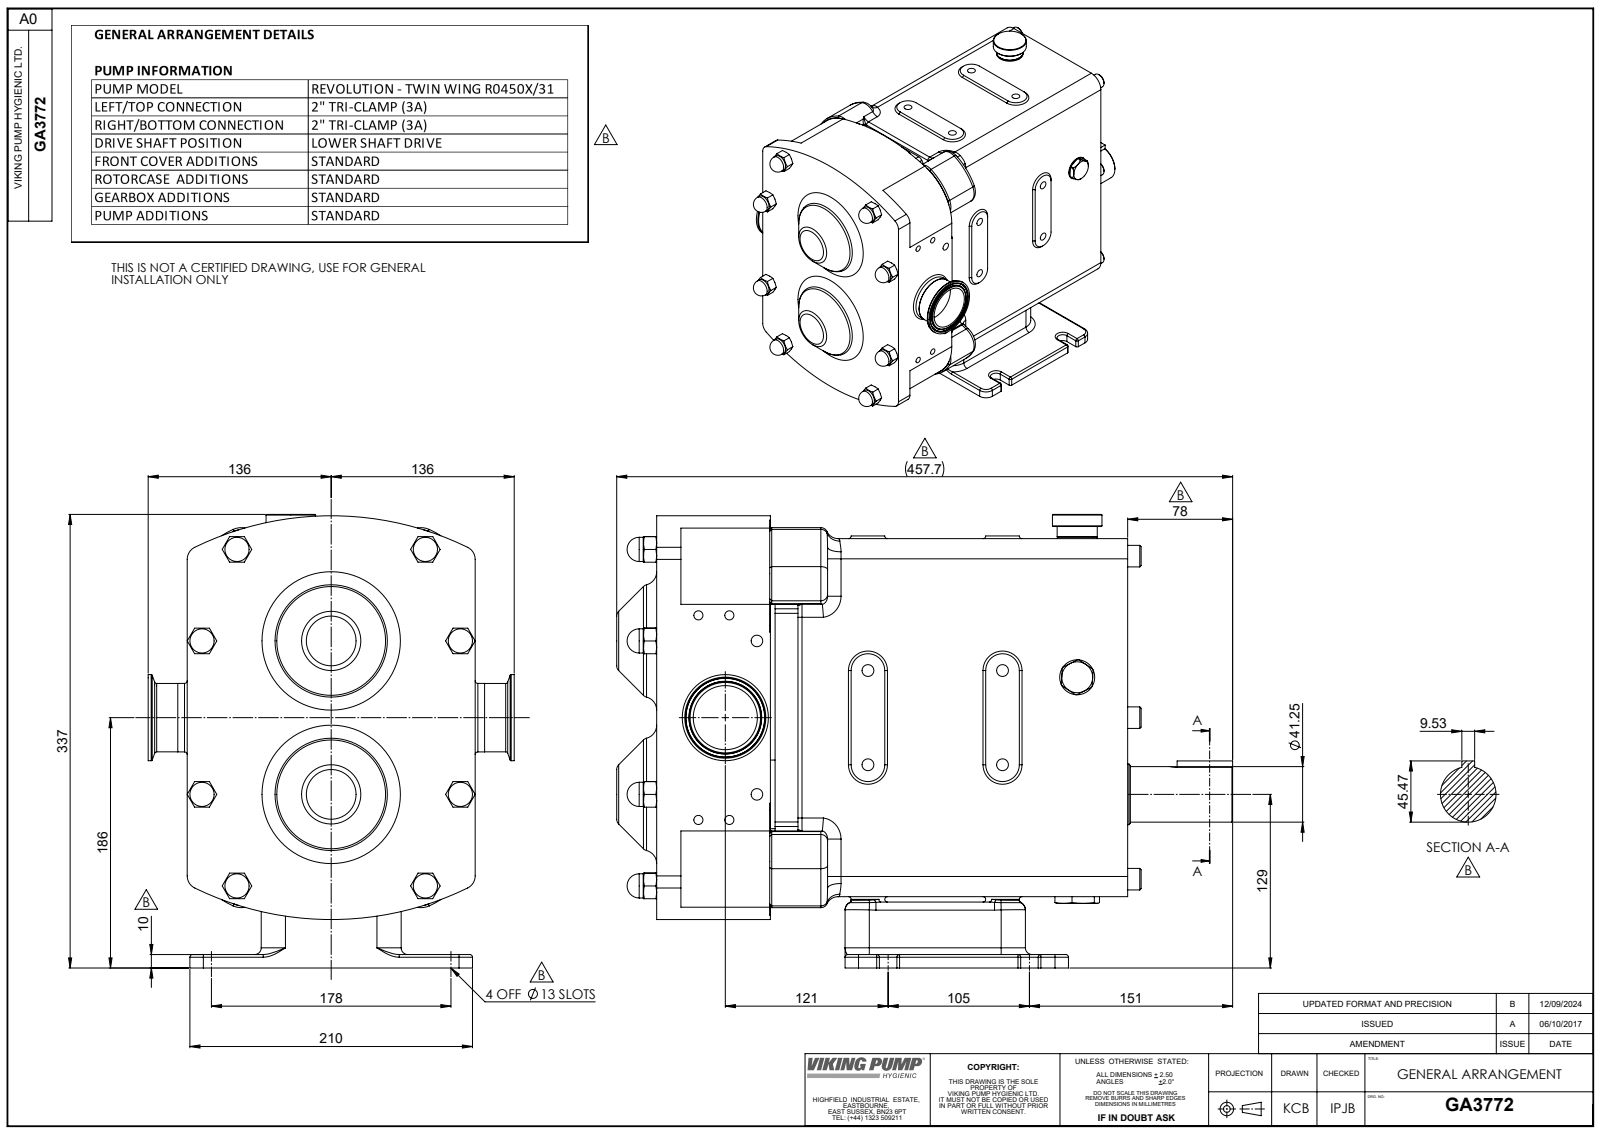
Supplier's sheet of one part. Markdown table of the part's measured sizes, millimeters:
| quantity | value |
| --- | --- |
| part name | Copy of RA94-5121-33M^GA3772; GA3772; Copy of R0450 CPP H BSD^GA3772 |
| STEP written by | SolidWorks 2023 (AUTOMOTIVE_DESIGN) |
| units | millimeters |
| bodies | 3 solids, 936 faces (288 planar, 273 cylindrical, 375 other) |
| overall size | 457.7 × 337 × 272 |
| volume | 16 630 000 mm³ |
| surface area | 668 385 mm² |
| round holes (diameter × count) | 8.8 × 8, 6.8 × 4, 8.6 × 2, 33.8 × 1, 47.65 × 1 |
| round bosses / shafts (diameter × count) | 18 × 8, 16 × 6, 64 × 1, 51 × 1, 50.9 × 1, 50.8 × 1, 45 × 1, 41.25 × 1 |
| partial cylindrical surfaces (radius × count) | 2 × 38, 10 × 30, 5 × 19, 5.9 × 8, 15 × 8, 18 × 8, 3 × 4, 6 × 4 |
| main face-to-face distances | 152, 84.5, 265.5, 350, 88, 3.5, 262, 266, 43, 183 |
| hole center spacings | 70, 100, 122.07, 23, 27.95, 47.47, 61.65, 76.06 |
